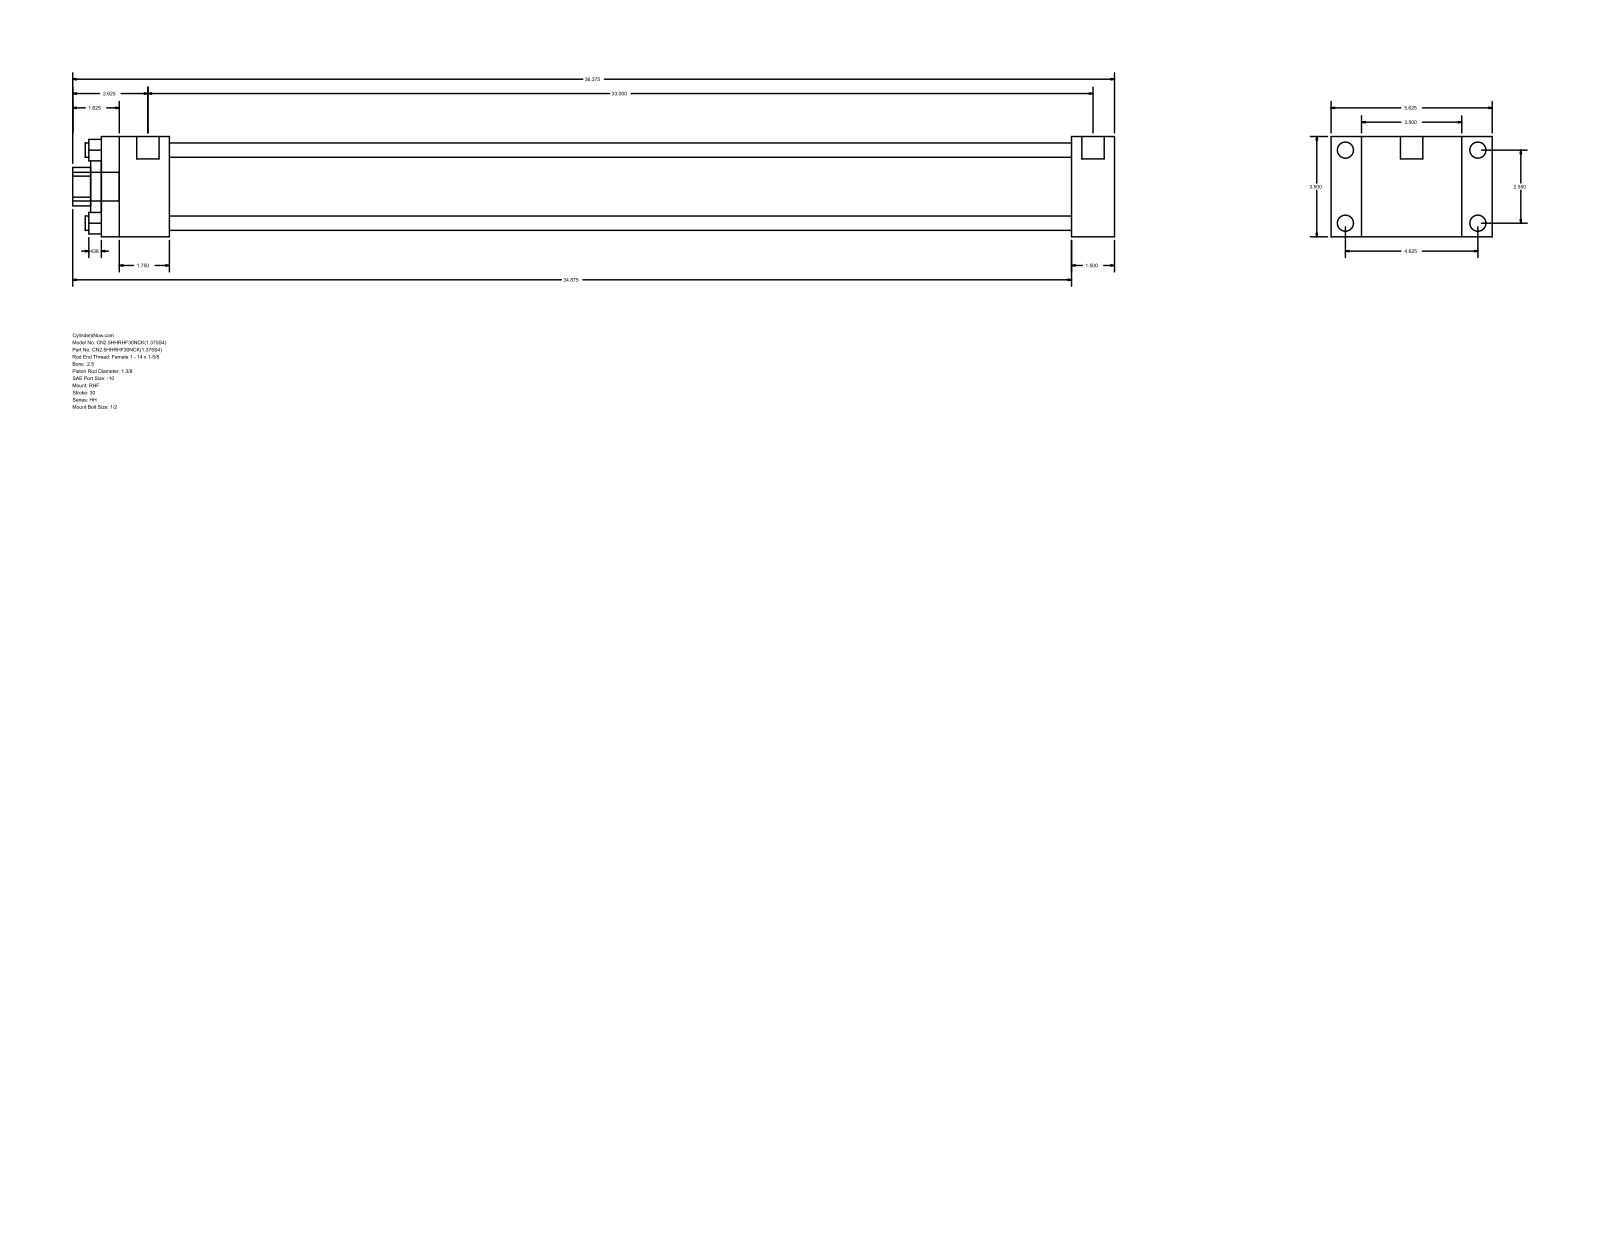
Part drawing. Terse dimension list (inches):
name: HH_RHF__0250_1.375
written by: GSSL Pune (CONFIG_CONTROL_DESIGN)
unit: in
bodies: 0 solids, 88 faces (60 planar, 28 cylindrical, 0 other)
size: 36.375 × 5.625 × 3.5
holes: 4× ⌀0.5, 1× ⌀1.375, 1× ⌀2, 1× ⌀2.875
bosses: 4× ⌀0.563, 4× ⌀0.219, 2× ⌀0.781, 1× ⌀1
rounds: 1× R0.672
face distances: 3.5, 1.5, 1.063, 4.563, 33.875, 35.375, 5.625, 2.375, 31.5, 33
hole spacings: 1.803, 2.55, 3.606
